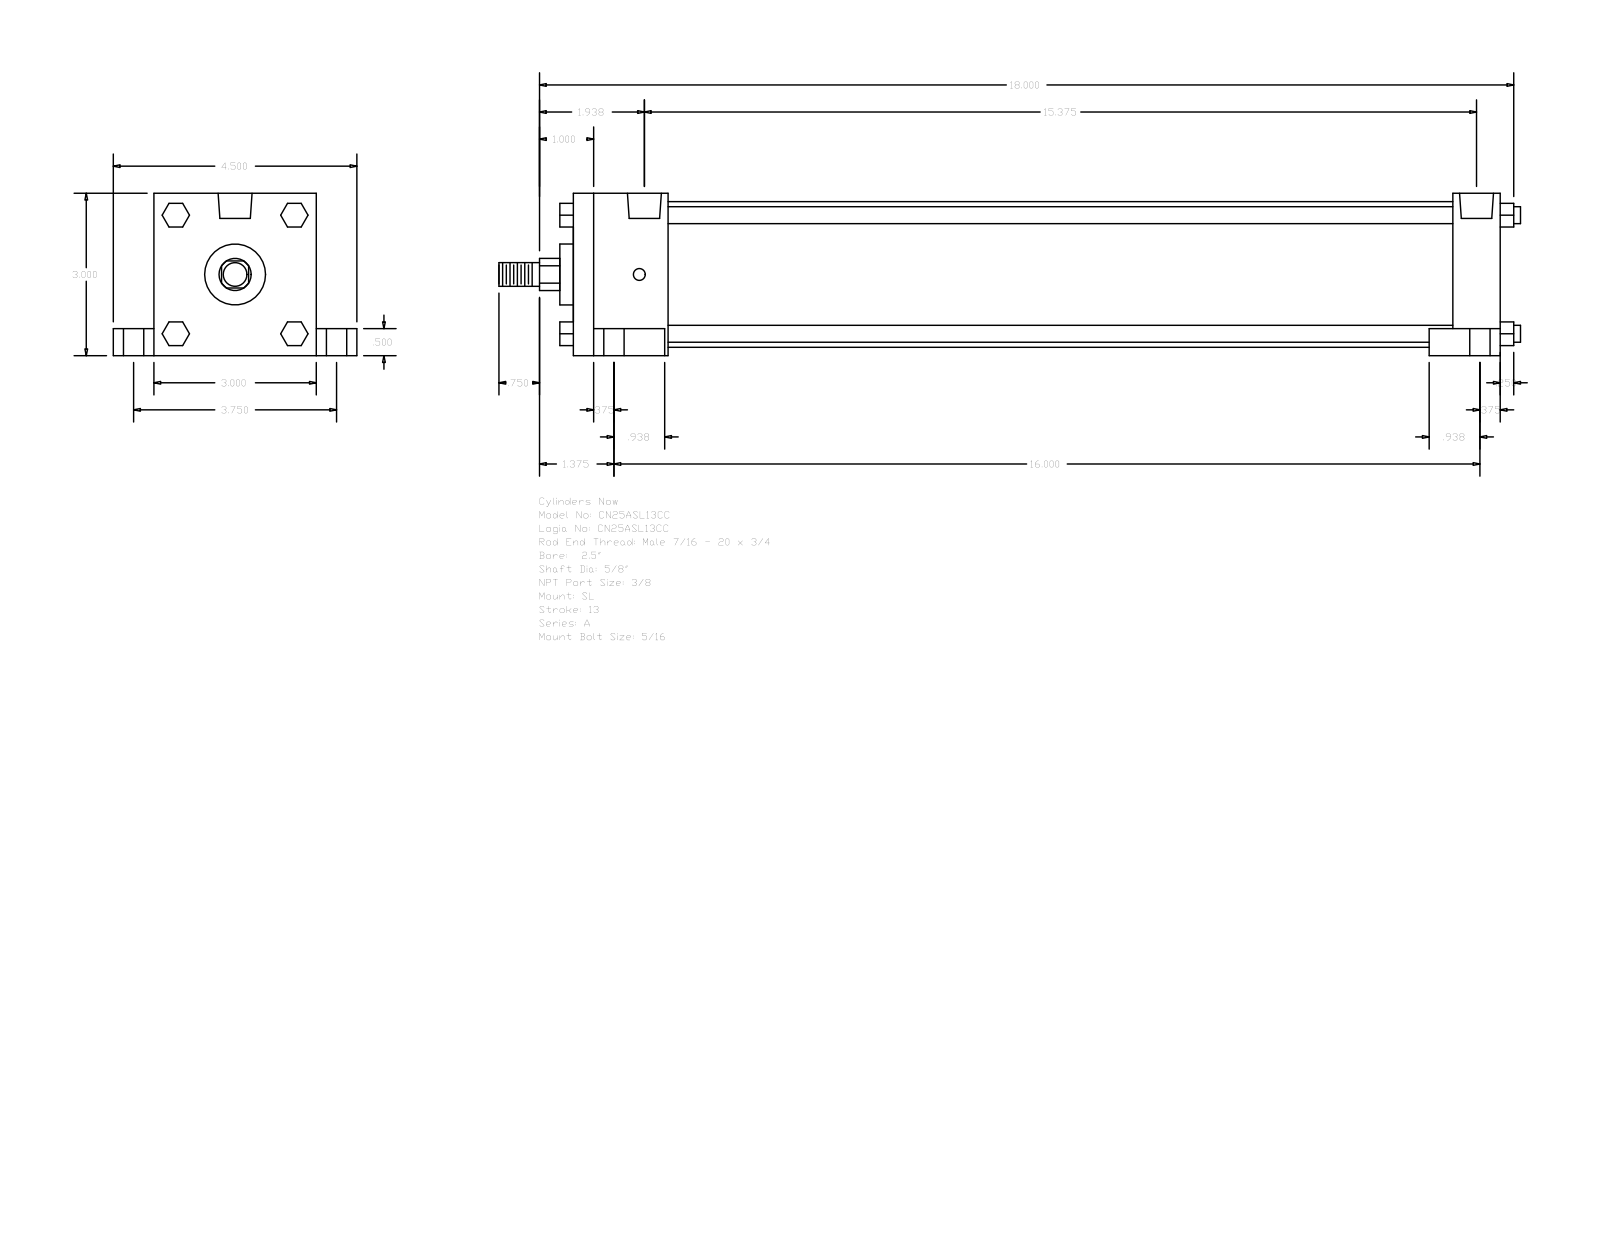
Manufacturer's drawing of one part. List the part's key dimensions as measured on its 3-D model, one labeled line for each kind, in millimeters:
Part name (STEP PRODUCT): A_SL__0250_0.625
STEP written by: GSSL Pune (CONFIG_CONTROL_DESIGN)
Units: millimetres
Bodies: 0 solids, 148 faces (112 planar, 36 cylindrical, 0 other)
Overall size (bounding box): 479.43 × 114.3 × 76.2
Round holes (diameter × count): ⌀5.56 ×4, ⌀9.53 ×4, ⌀15.88 ×4, ⌀15.93 ×2
Round bosses / shafts (diameter × count): ⌀7.94 ×4, ⌀68.33 ×1, ⌀28.57 ×1, ⌀15.88 ×1, ⌀11.11 ×1
Partial cylindrical surfaces — rounded edges, fillets, slot ends (radius × count): R7.54 ×1
Main face-to-face distances: 76.2, 434.97, 44.45, 390.52, 412.74, 368.29, 22.23, 63.5, 12.7, 19.05
Hole centre spacings: 2.38, 47.63, 47.65, 49.09, 49.72, 95.24, 392.91, 394.99
